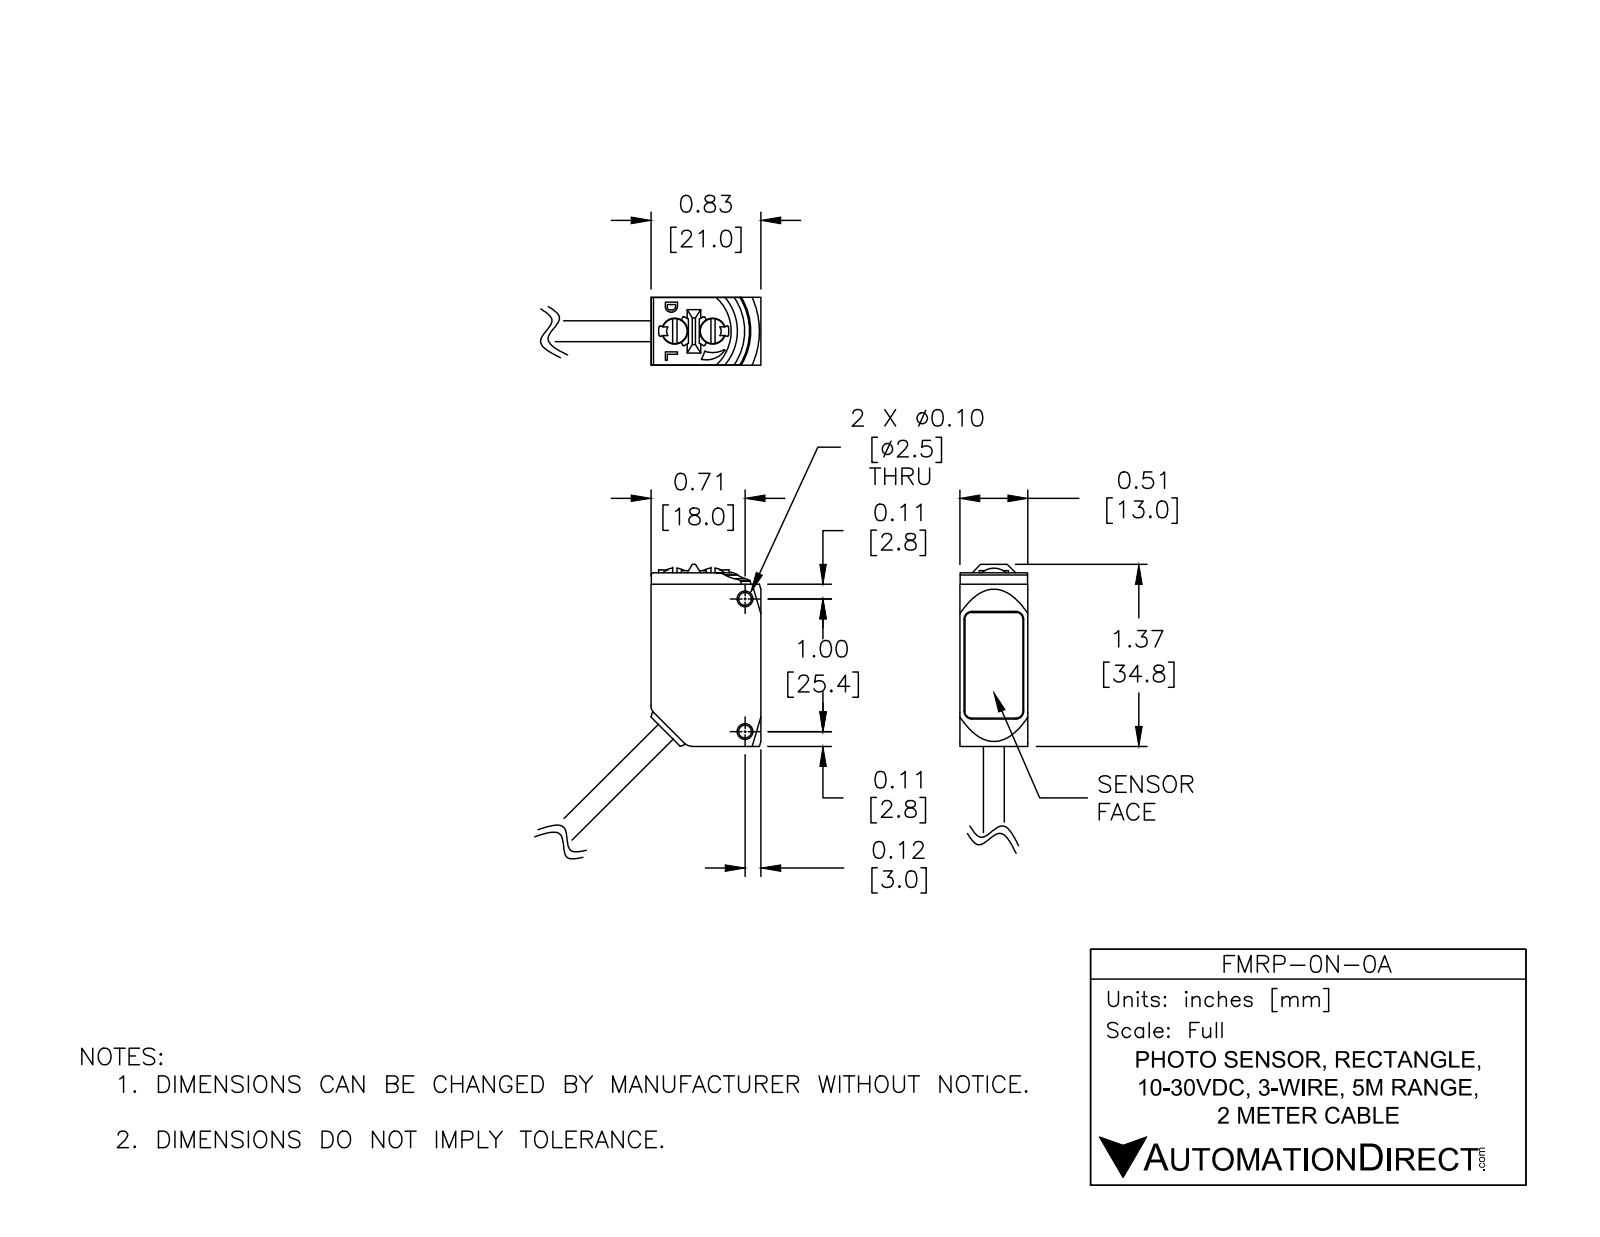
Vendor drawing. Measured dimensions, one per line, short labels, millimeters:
name: FMRP-0N-0A
written by: SolidWorks 2017 (AUTOMOTIVE_DESIGN)
unit: mm
bodies: 1 solid, 186 faces (89 planar, 72 cylindrical, 25 other)
size: 52.9 × 39.1 × 13
volume: 8 880 mm³; area: 3 533 mm²
holes: 2× ⌀2.5, 2× ⌀5
bosses: 2× ⌀4.8, 1× ⌀4
rounds: 7× R0.5, 7× R0.5, 4× R0.2, 4× R0.3, 4× R1.3, 4× R1.5, 3× R0.1, 2× R0.5
face distances: 13, 21, 33.2, 0.9, 13, 0.8, 12.2, 0.9, 12, 12
hole spacings: 7.3, 25.4
